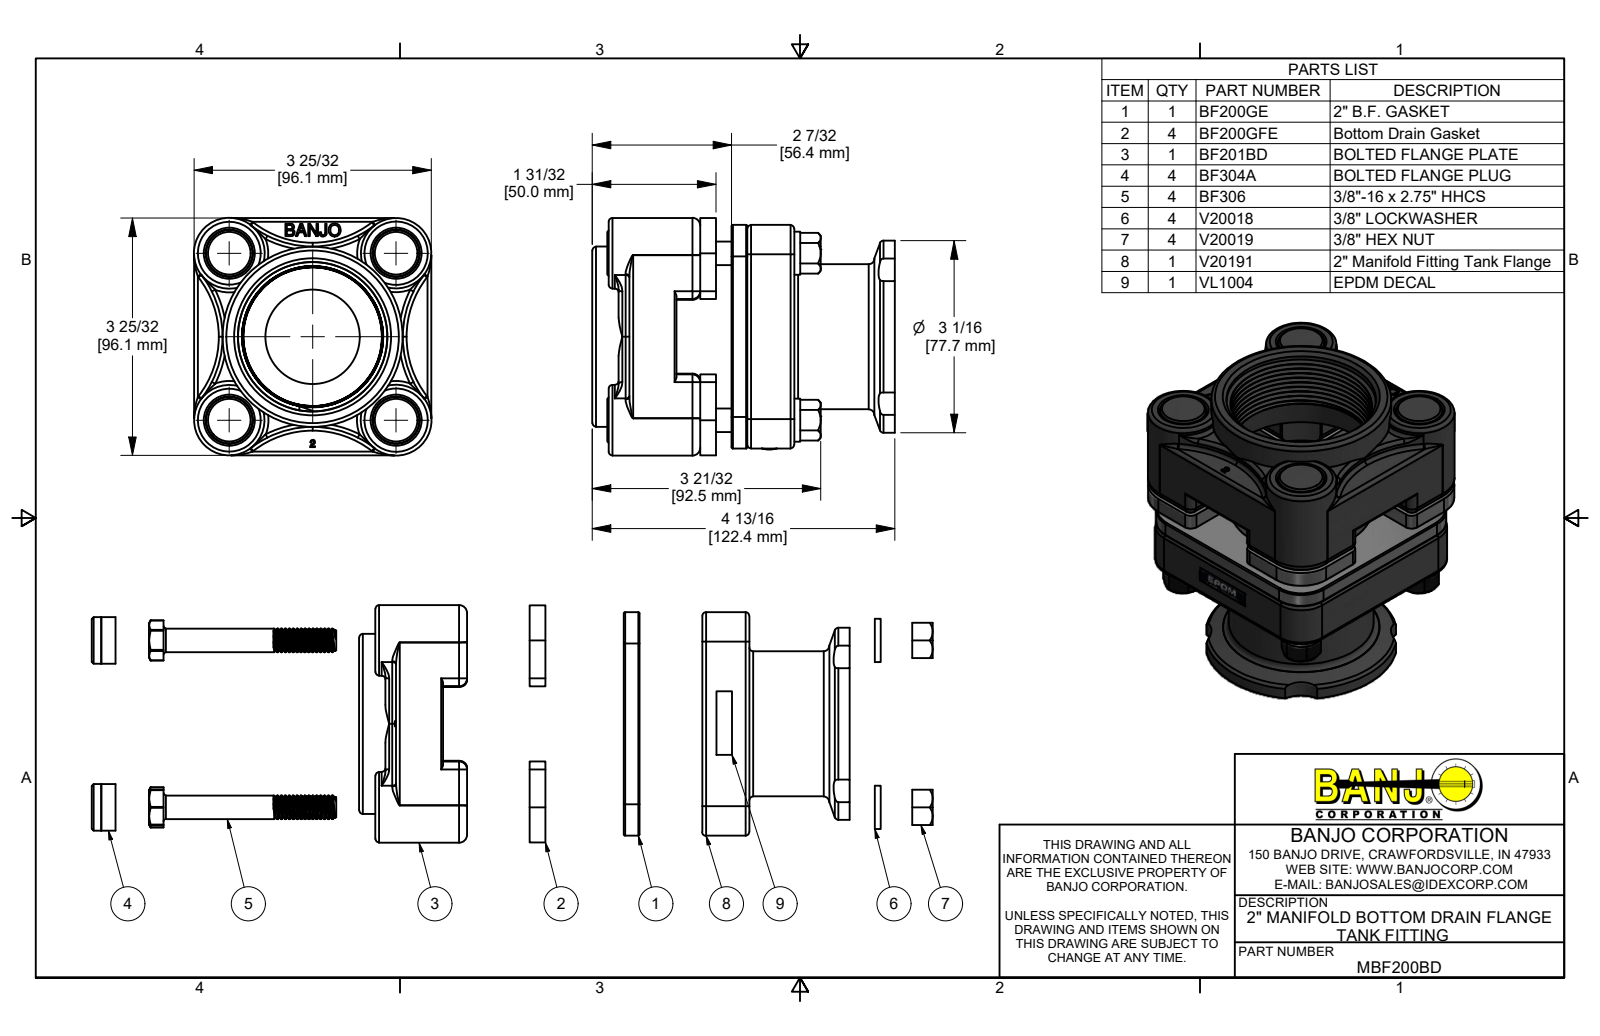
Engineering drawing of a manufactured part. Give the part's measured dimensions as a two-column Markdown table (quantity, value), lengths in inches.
| quantity | value |
| --- | --- |
| part name | MBF200BD; BF201BD; V20191; BF200GFE (+6 more) |
| STEP written by | Autodesk Inventor 2019 (AUTOMOTIVE_DESIGN) |
| units | inches |
| bodies | 24 solids, 1233 faces (359 planar, 411 cylindrical, 463 other) |
| overall size | 4.82 × 3.784 × 3.784 |
| volume | 28.85 in³ |
| surface area | 202.1 in² |
| round holes (diameter × count) | 0.307 × 4, 0.38 × 4, 0.385 × 4, 0.406 × 4, 0.41 × 4, 0.422 × 4, 0.715 × 4, 0.75 × 4, 1.5 × 1, 2.19 × 1, 2.25 × 1 |
| round bosses / shafts (diameter × count) | 0.324 × 60, 1.125 × 4, 0.742 × 4, 0.687 × 4, 0.375 × 4, 2.87 × 1, 2.31 × 1 |
| partial cylindrical surfaces (radius × count) | 0.125 × 41, 0.06 × 20, 0.02 × 16, 0.162 × 8, 1.19 × 5, 0.03 × 4, 0.32 × 4, 0.45 × 4 |
| main face-to-face distances | 0.25, 0.75, 0.5, 1.5, 0.111, 3.671, 1, 1.25, 1.88, 1.13 |
| hole center spacings | 1.88, 2.659, 3.761 |
